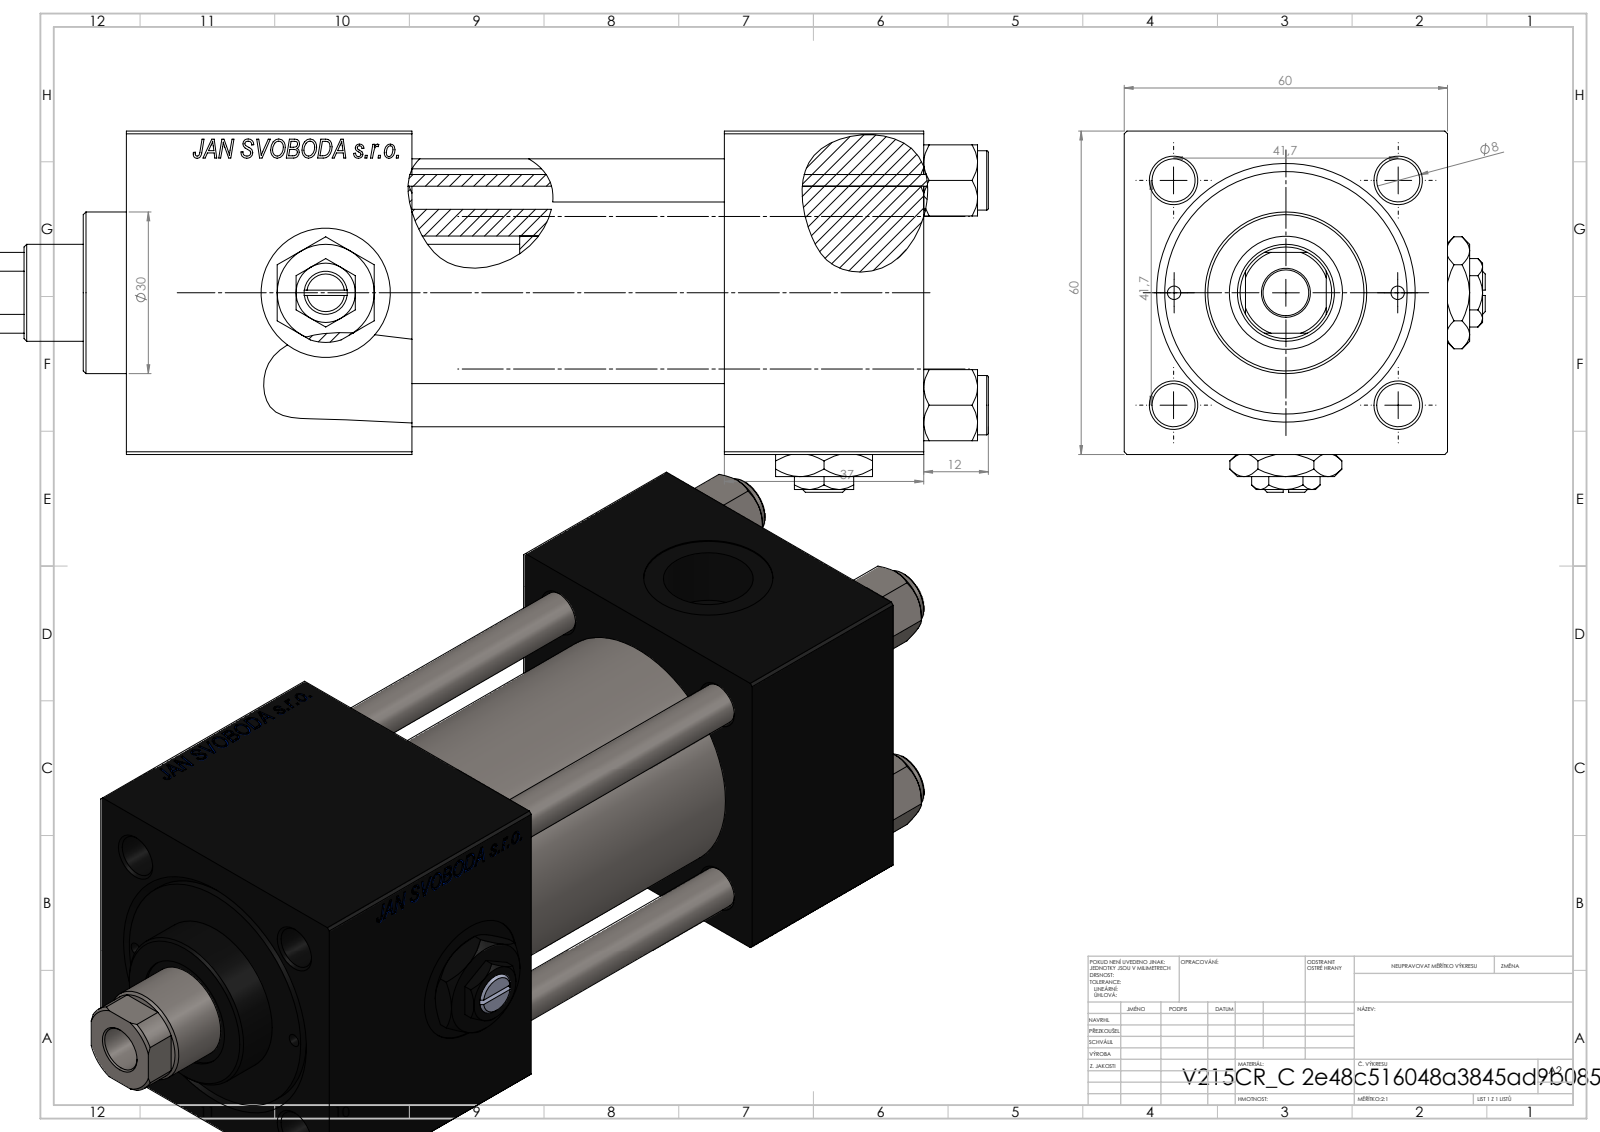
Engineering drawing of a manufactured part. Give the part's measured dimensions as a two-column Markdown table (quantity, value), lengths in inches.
| quantity | value |
| --- | --- |
| part name | NUT_M5_C; V215CR_C_TYCINKA; Zatka_pro_OIL_PORT; V215CR_C_Body (+2 more) |
| STEP written by | SolidWorks 2019 (CONFIG_CONTROL_DESIGN) |
| units | inches |
| bodies | 13 solids, 1256 faces (576 planar, 102 cylindrical, 578 other) |
| overall size | 7.283 × 2.638 × 2.638 |
| volume | 24.34 in³ |
| surface area | 168 in² |
| round holes (diameter × count) | 0.315 × 4, 0.098 × 2, 0.276 × 2, 0.656 × 2, 0.945 × 2, 0.335 × 1, 0.709 × 1, 0.827 × 1, 1.22 × 1, 1.575 × 1, 1.772 × 1 |
| round bosses / shafts (diameter × count) | 0.433 × 4, 1.811 × 1, 1.181 × 1 |
| partial cylindrical surfaces (radius × count) | 0.335 × 1 |
| main face-to-face distances | 2.362, 1.457, 2.087, 5.827, 4.37, 2.283, 3.74, 4.697, 3.24, 0.957 |
| hole center spacings | 0.821, 1.161, 1.642, 1.832, 0.817, 2.322, 1.634 |
